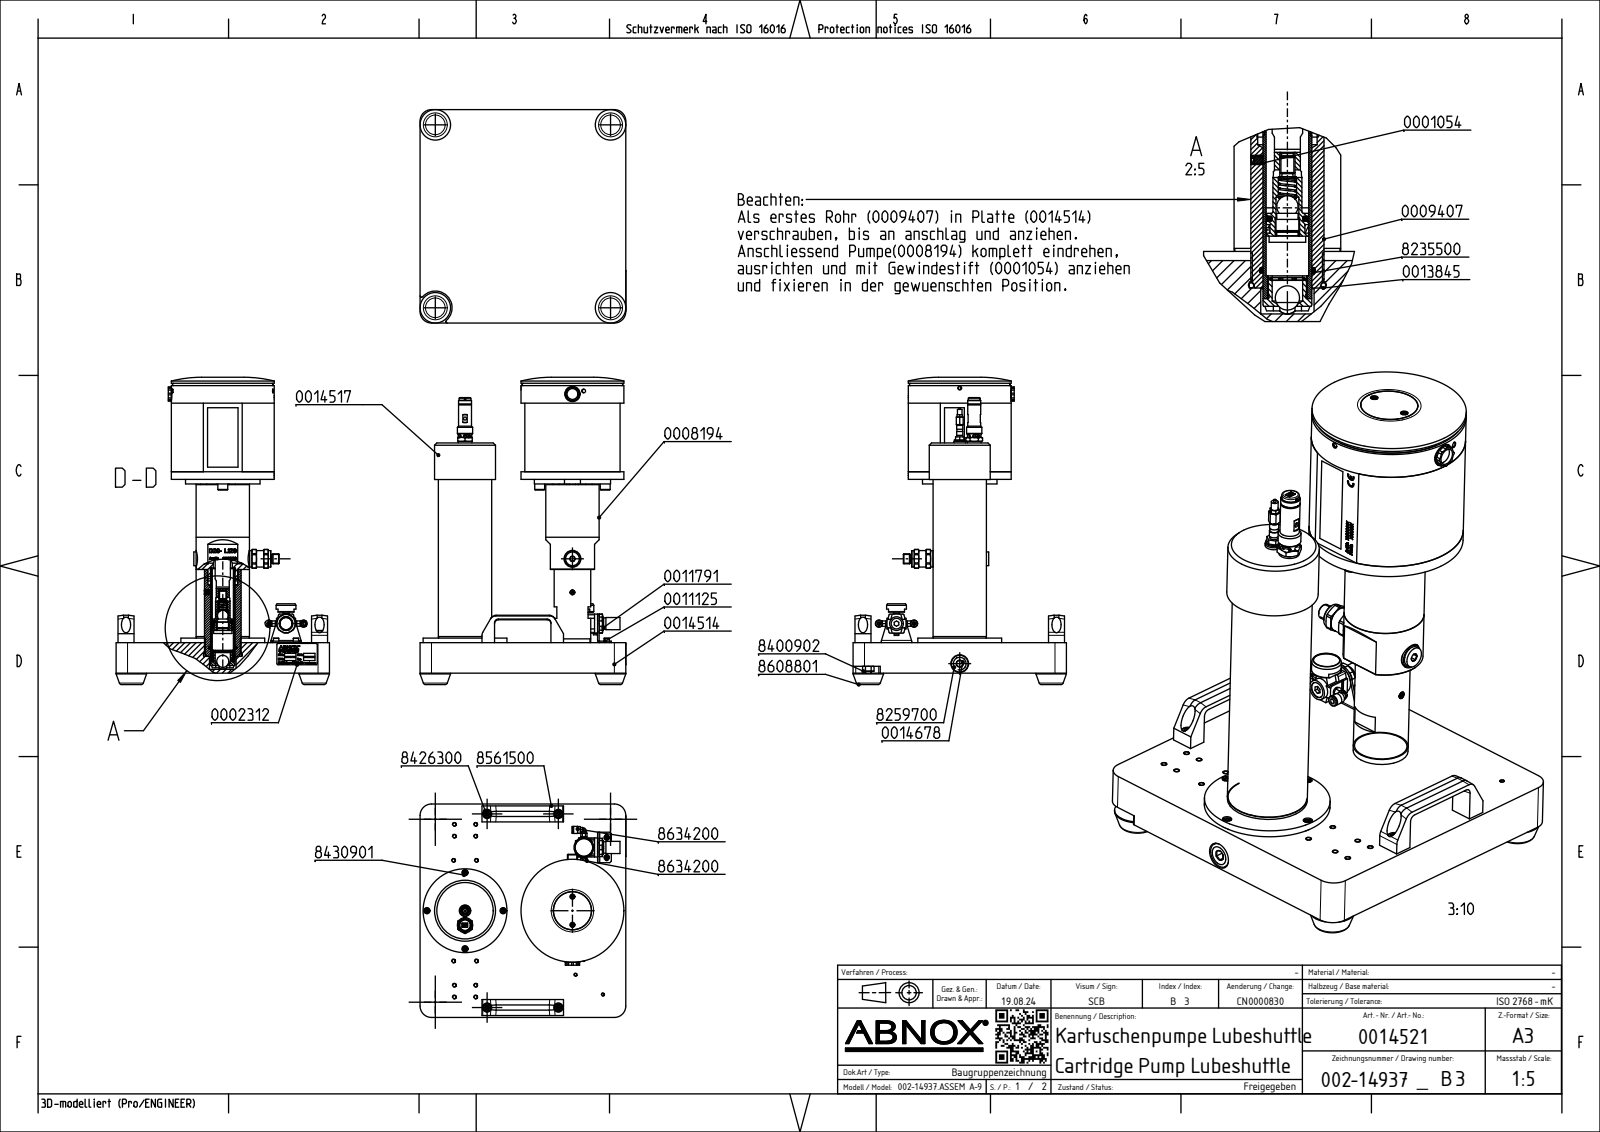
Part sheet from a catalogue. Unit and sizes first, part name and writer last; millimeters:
Units: millimetres
Overall size (bounding box): 403.2 × 280 × 270.2
Round holes (diameter × count): ⌀12 ×4, ⌀4 ×3, ⌀14 ×1
Round bosses / shafts (diameter × count): ⌀40 ×4, ⌀18 ×3, ⌀7 ×3, ⌀70 ×2, ⌀15 ×2, ⌀13 ×2, ⌀9.3 ×2, ⌀9.1 ×2
Partial cylindrical surfaces — rounded edges, fillets, slot ends (radius × count): R8 ×12, R5 ×10, R1.08 ×8, R1.5 ×5, R2 ×4, R15 ×4, R1 ×2, R2.4 ×2
Main face-to-face distances: 40, 6, 90, 208.2, 123, 264.2, 23, 26.1, 10, 100
Hole centre spacings: 93.5, 254, 270.66, 111.83, 148.85, 163.31, 190.58
Bodies: 0 solids, 649 faces (244 planar, 233 cylindrical, 172 other)
Part name (STEP PRODUCT): 002-14937
STEP written by: CREO PARAMETRIC BY PTC INC, 2023254 (CONFIG_CONTROL_DESIGN)
